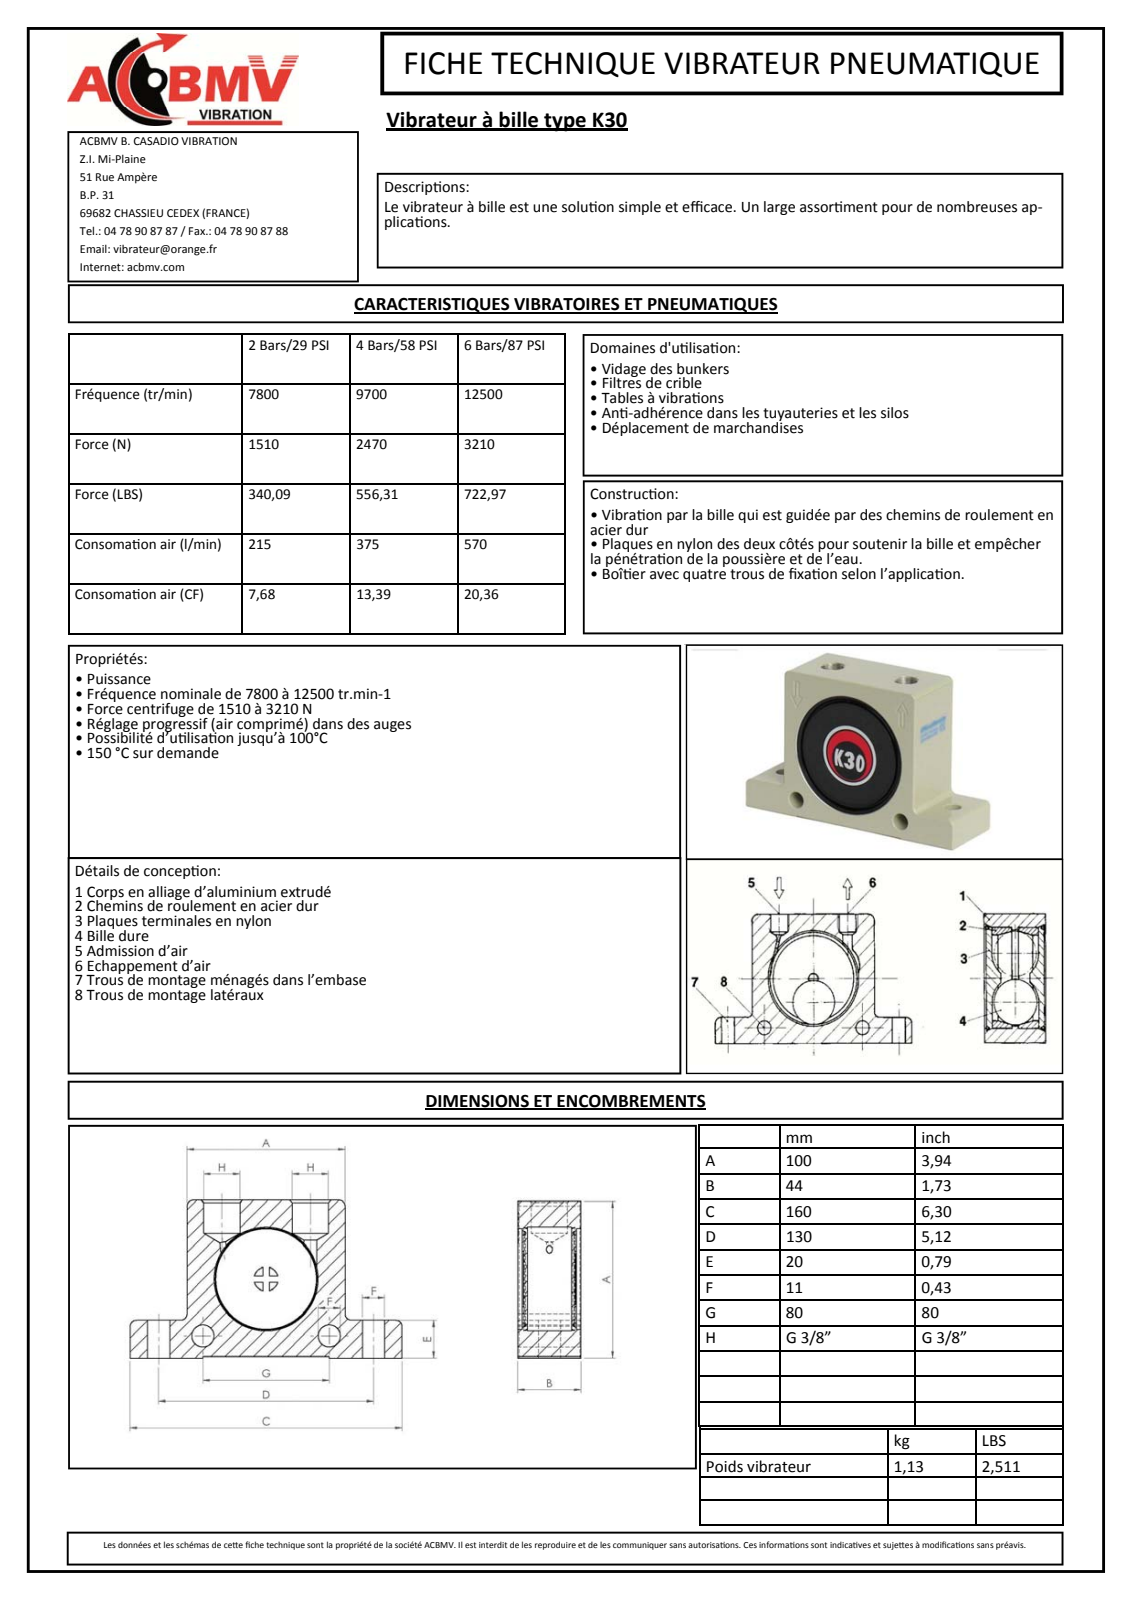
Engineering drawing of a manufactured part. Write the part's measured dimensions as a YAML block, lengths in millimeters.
part_name: "1030-00-M"
step_written_by: "Autodesk Inventor 2011 (CONFIG_CONTROL_DESIGN)"
units: millimeters
bodies: {solids: 1, faces: 376, planar: 222, cylindrical: 104, other: 50}
overall_size: [160, 100, 44]
volume: 281575
surface_area: 76636
round_holes:
  - {diameter: 11, count: 4}
  - {diameter: 14.95, count: 2}
  - {diameter: 3.1, count: 1}
  - {diameter: 3.34, count: 1}
  - {diameter: 7, count: 1}
  - {diameter: 26, count: 1}
  - {diameter: 36, count: 1}
  - {diameter: 41.5, count: 1}
  - {diameter: 79.8, count: 1}
  - {diameter: 80.8, count: 1}
round_bosses_or_shafts:
  - {diameter: 70.5, count: 1}
  - {diameter: 40, count: 1}
  - {diameter: 34.2, count: 1}
  - {diameter: 3, count: 1}
partial_cylinders:
  - {radius: 0.3, count: 14}
  - {radius: 19.5, count: 8}
  - {radius: 4, count: 6}
  - {radius: 0.55, count: 4}
  - {radius: 0.86, count: 4}
  - {radius: 1.5, count: 4}
  - {radius: 2, count: 4}
  - {radius: 3.5, count: 4}
face_to_face_distances: [39.5, 4.5, 0.5, 100, 44, 39, 43.5, 4, 35, 43]
hole_center_spacings: [37, 52.5, 55.17, 93, 4, 56, 80, 130]
